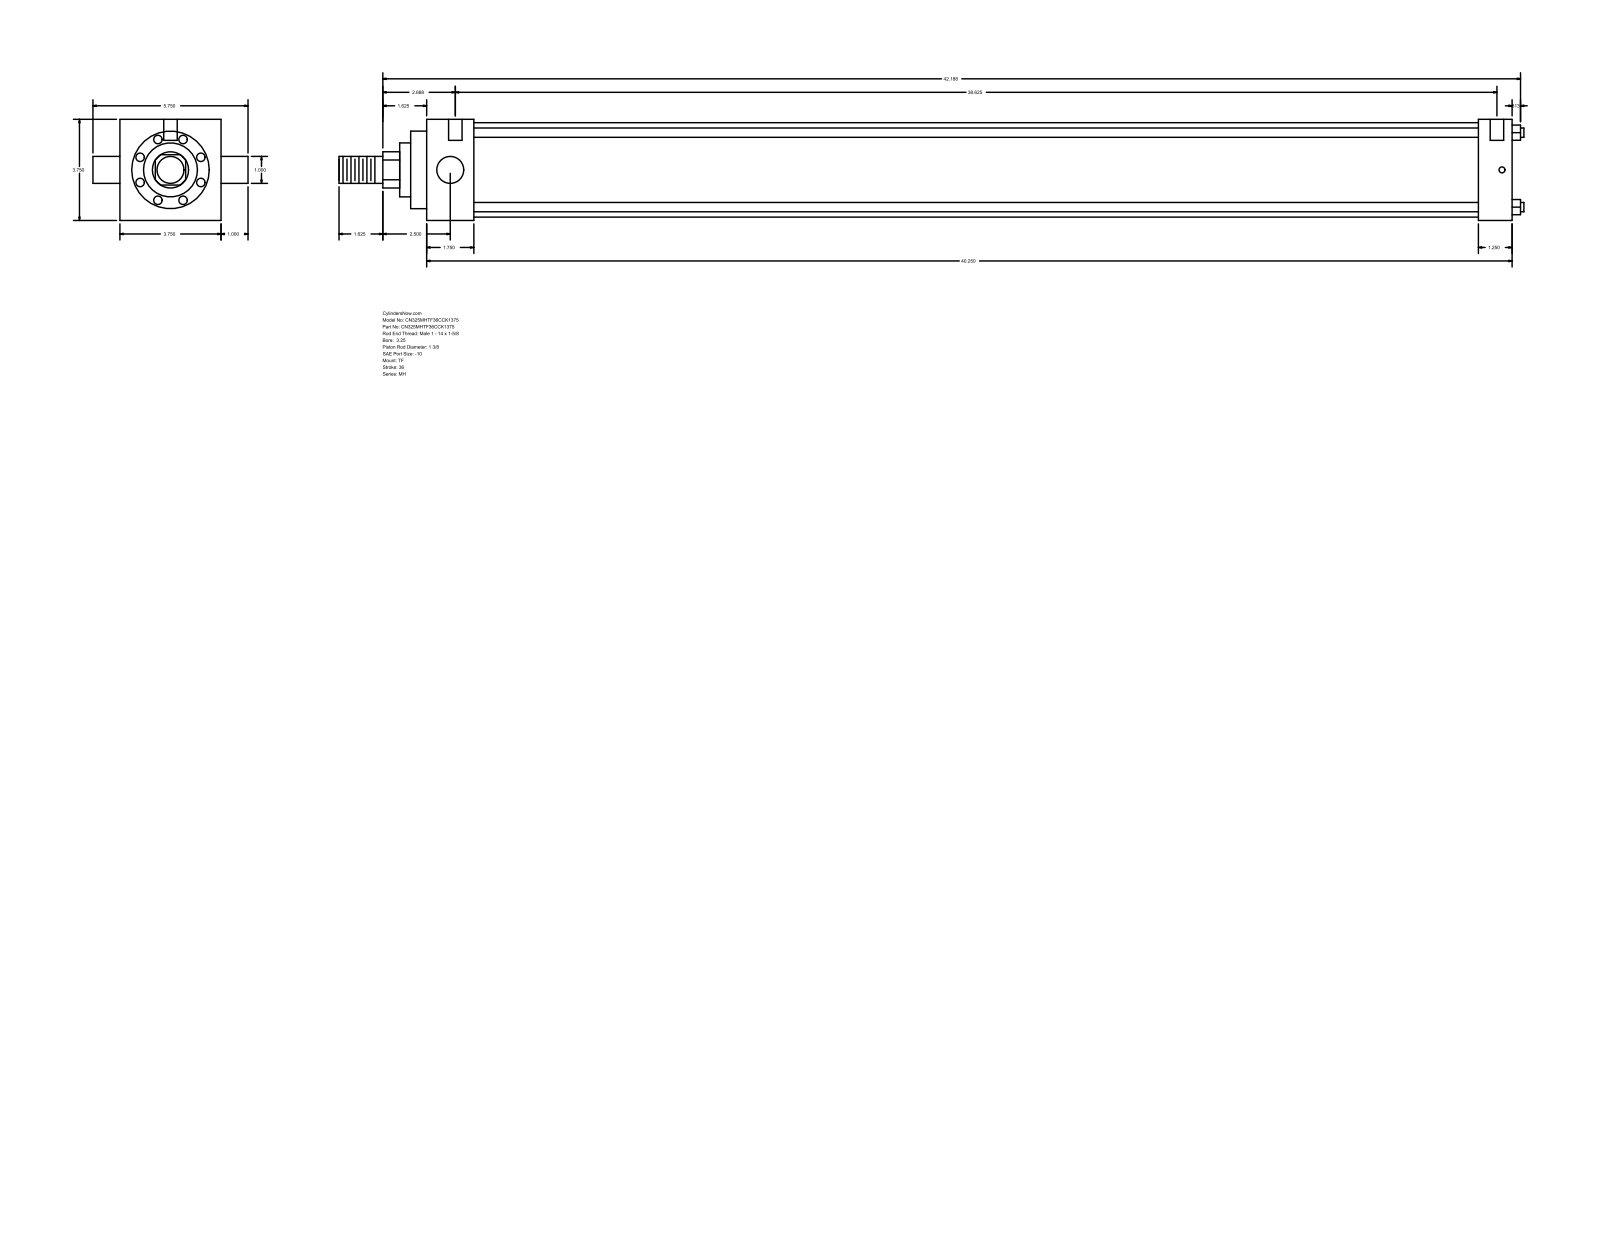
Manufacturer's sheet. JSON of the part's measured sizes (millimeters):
{"part_name": "MH_TF__0325_1.375", "step_written_by": "GSSL Pune (CONFIG_CONTROL_DESIGN)", "units": "millimeters", "bodies": {"solids": 0, "faces": 86, "planar": 61, "cylindrical": 25, "other": 0}, "overall_size": [1116.01, 146.05, 95.25], "round_holes": [[5.56, 3], [12.7, 2]], "round_bosses_or_shafts": [[8.76, 4], [25.4, 2], [88.9, 1], [73.03, 1], [50.8, 1], [34.92, 1]], "partial_cylinders_radius": [[17.06, 1]], "face_to_face_distances": [95.24, 1022.35, 44.45, 990.61, 946.16, 977.9, 31.74, 15.08, 59.53, 1005.69], "hole_center_spacings": [1.59, 4.76, 981.08, 982.67, 985.84, 987.43]}
